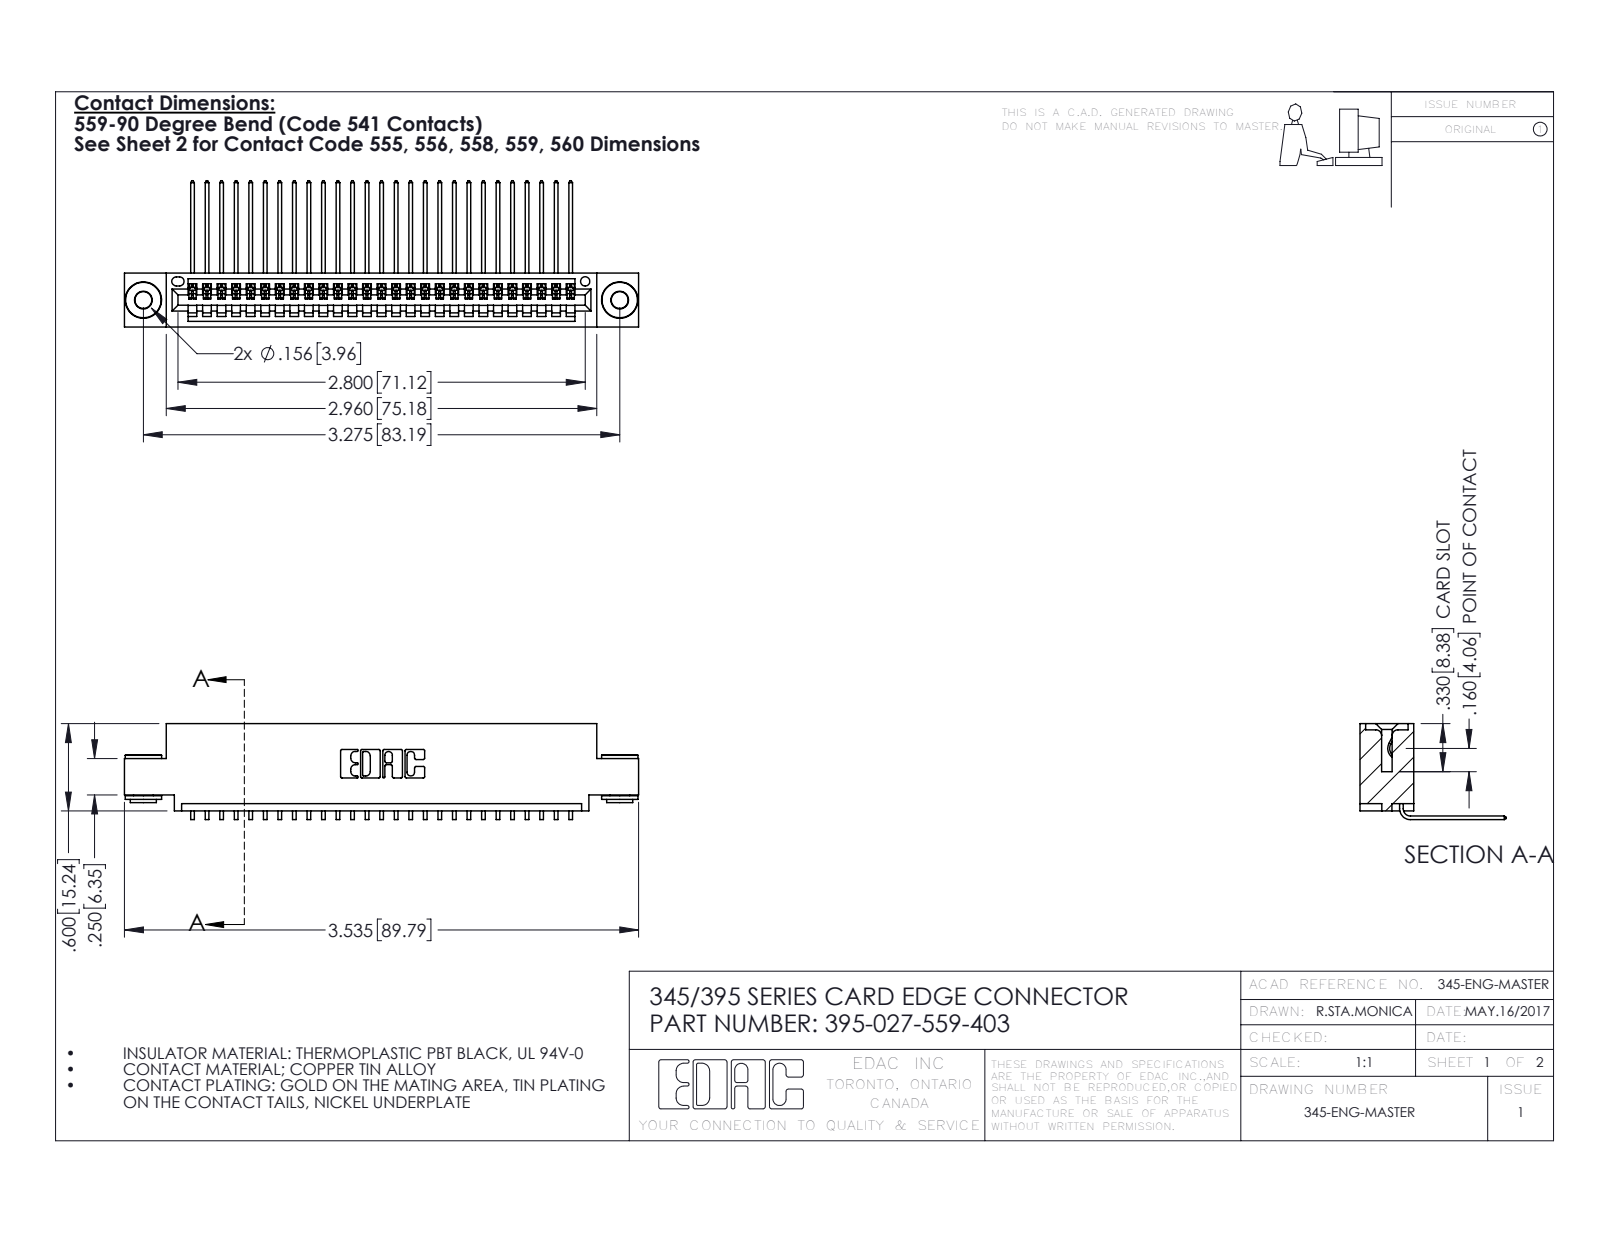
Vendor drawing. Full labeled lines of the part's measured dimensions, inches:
Part name (STEP PRODUCT): 345-250-002_345-250-002-102; 345-292-001_558 559 Tail - 1; 345 Part_0.110 Offset - 0.156 Dia-TH; 395-027-559-403
STEP written by: SolidWorks 2016 (CONFIG_CONTROL_DESIGN)
Units: inches
Bodies: 30 solids, 1788 faces (1228 planar, 552 cylindrical, 8 other)
Overall size (bounding box): 3.535 × 1.005 × 0.659
Volume: 0.515 in³ · Surface area: 18.35 in²
Round holes (diameter × count): ⌀0.116 ×2, ⌀0.156 ×2, ⌀0.064 ×1
Round bosses / shafts (diameter × count): ⌀0.25 ×2, ⌀0.18 ×2, ⌀0.136 ×2
Partial cylindrical surfaces — rounded edges, fillets, slot ends (radius × count): R0.006 ×54, R0.01 ×22, R0.007 ×6, R0.031 ×6, R0.026 ×3, R0.031 ×2, R0.04 ×2, R0.014 ×1
Main face-to-face distances: 0.072, 0.298, 0.37, 0.2, 0.025, 0.098, 0.272, 0.225, 0.149, 0.072
Hole centre spacings: 0.27, 3.04, 3.275
